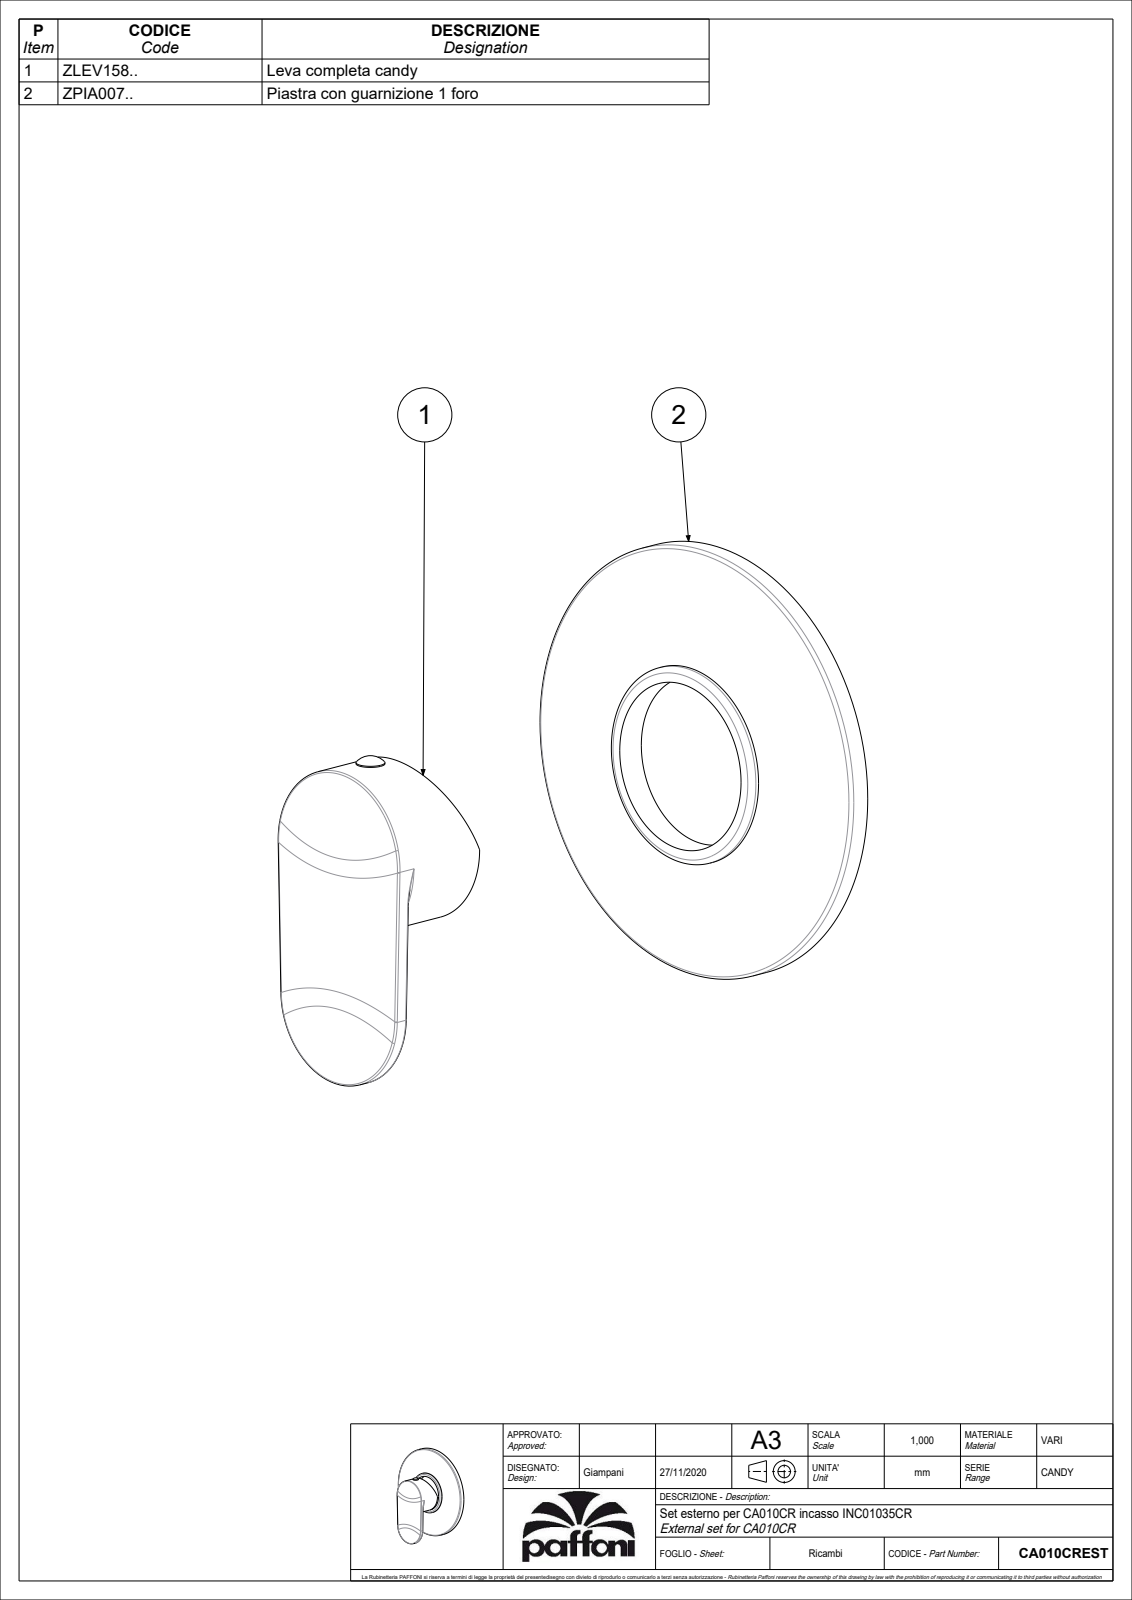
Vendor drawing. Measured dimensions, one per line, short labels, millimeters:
name: CA010CREST
written by: CREO PARAMETRIC BY PTC INC, 2020044 (CONFIG_CONTROL_DESIGN)
unit: mm
bodies: 2 solids, 153 faces (48 planar, 43 cylindrical, 62 other)
size: 120.5 × 116 × 44.5
volume: 33 333 mm³; area: 40 428 mm²
holes: 1× ⌀3, 1× ⌀45, 1× ⌀50, 1× ⌀114
bosses: 1× ⌀116, 1× ⌀53, 1× ⌀7.6, 1× ⌀5.5
rounds: 4× R1, 4× R3, 1× R3.5, 1× R21.5
face distances: 4, 2.45, 11.55, 30, 11.5, 41.5, 9.1, 1.5, 2.5, 3.5
